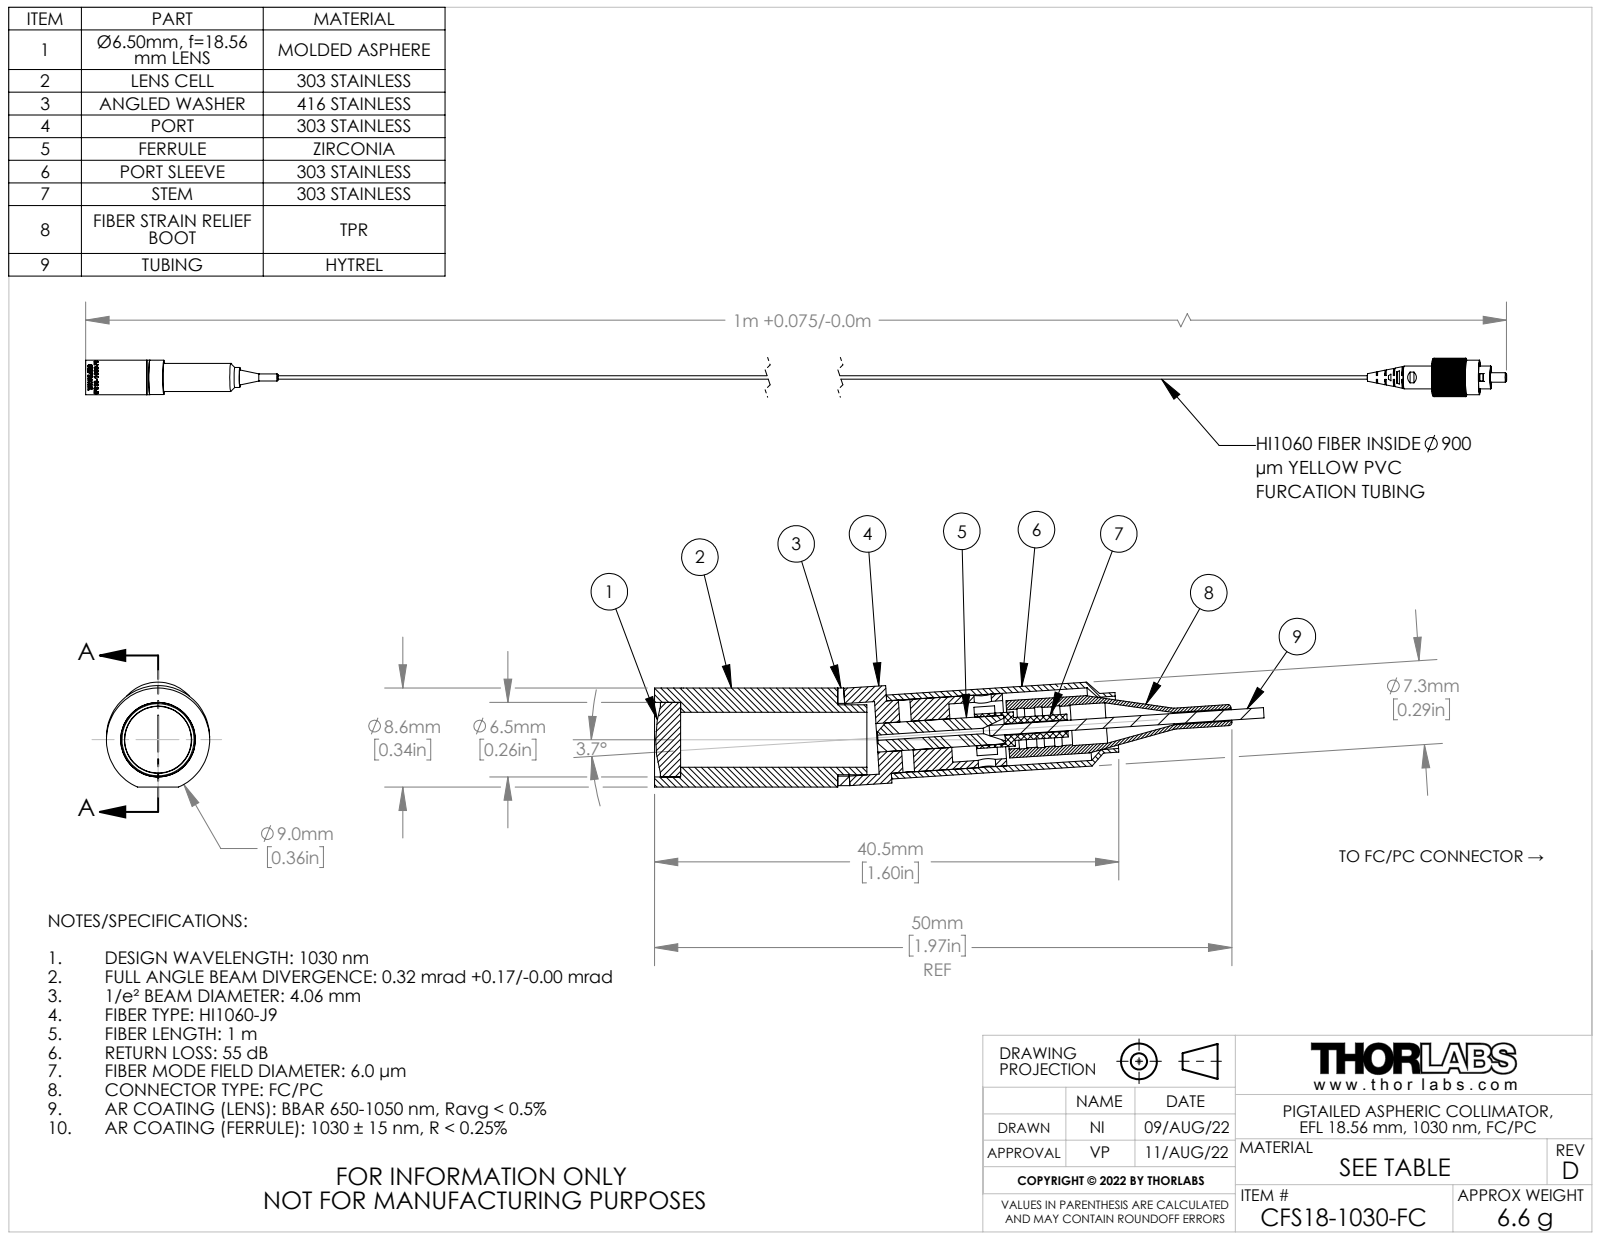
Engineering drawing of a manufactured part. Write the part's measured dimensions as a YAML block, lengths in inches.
part_name: "17369-E0W"
step_written_by: "SolidWorks 2018 (CONFIG_CONTROL_DESIGN)"
units: inches
bodies: {solids: 12, faces: 528, planar: 254, cylindrical: 222, other: 52}
overall_size: [40.889, 2.933, 0.393]
volume: 0.179
surface_area: 12.75
round_holes:
  - {diameter: 0.04, count: 2}
  - {diameter: 0.059, count: 2}
  - {diameter: 0.2, count: 2}
  - {diameter: 0.25, count: 2}
  - {diameter: 0.018, count: 1}
  - {diameter: 0.039, count: 1}
  - {diameter: 0.042, count: 1}
  - {diameter: 0.055, count: 1}
  - {diameter: 0.098, count: 1}
  - {diameter: 0.098, count: 1}
  - {diameter: 0.119, count: 1}
  - {diameter: 0.12, count: 1}
round_bosses_or_shafts:
  - {diameter: 0.098, count: 2}
  - {diameter: 0.355, count: 1}
  - {diameter: 0.354, count: 1}
  - {diameter: 0.289, count: 1}
  - {diameter: 0.28, count: 1}
  - {diameter: 0.256, count: 1}
  - {diameter: 0.249, count: 1}
  - {diameter: 0.24, count: 1}
partial_cylinders:
  - {radius: 0.089, count: 1}
  - {radius: 0.117, count: 1}
  - {radius: 0.197, count: 1}
face_to_face_distances: [0.267, 39.71, 0.267, 0.145, 39.648, 0.062, 39.503, 39.565, 39.75, 39.605]
hole_center_spacings: [0.02, 0.02, 0.27, 0.02]
